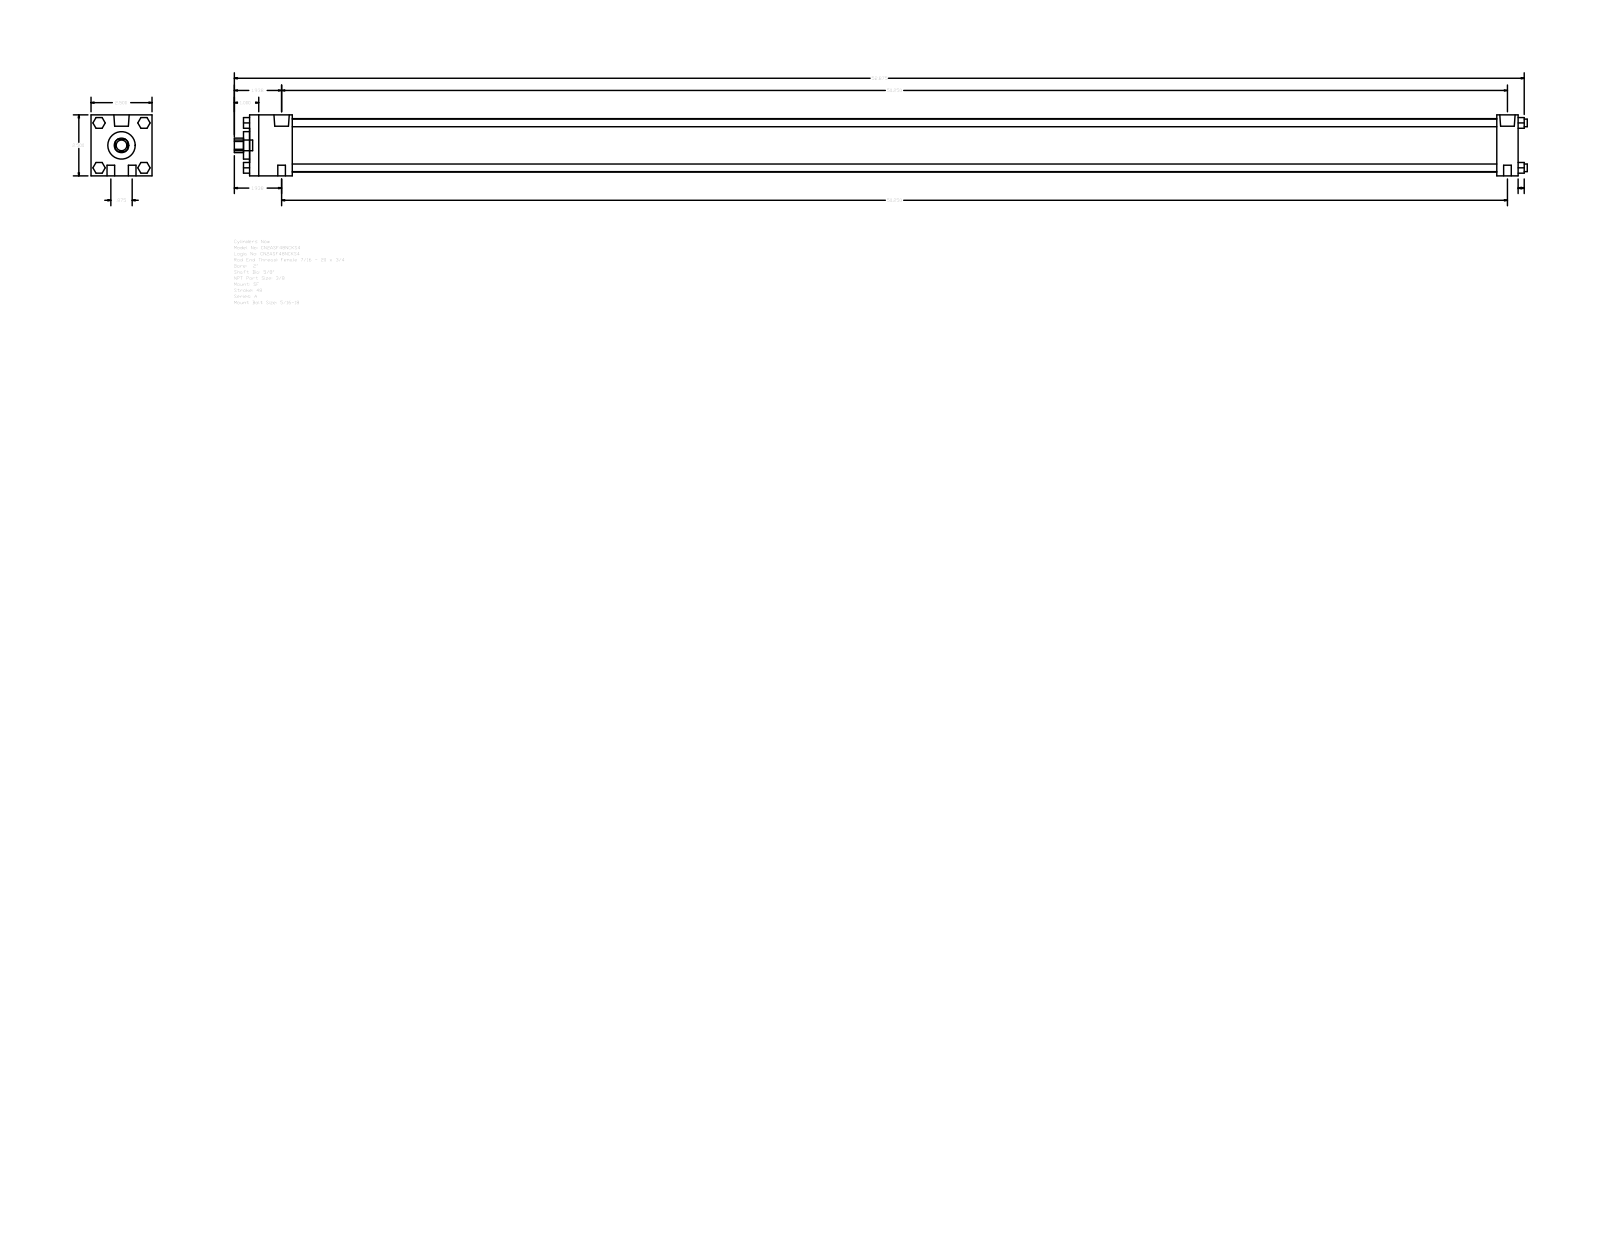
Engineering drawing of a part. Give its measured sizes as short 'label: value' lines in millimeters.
name: A_SF__0200_0.625
written by: GSSL Pune (CONFIG_CONTROL_DESIGN)
unit: mm
bodies: 0 solids, 124 faces (94 planar, 30 cylindrical, 0 other)
size: 1346.2 × 63.5 × 63.5
holes: 1× ⌀15.88, 1× ⌀28.57, 1× ⌀55.63
bosses: 8× ⌀7.94, 2× ⌀15.93, 2× ⌀5.56, 1× ⌀11.11
rounds: 1× R7.54
face distances: 63.5, 1320.79, 1298.57, 22.22, 44.45, 1254.12, 1276.34, 50.8, 6.35, 1304.92
